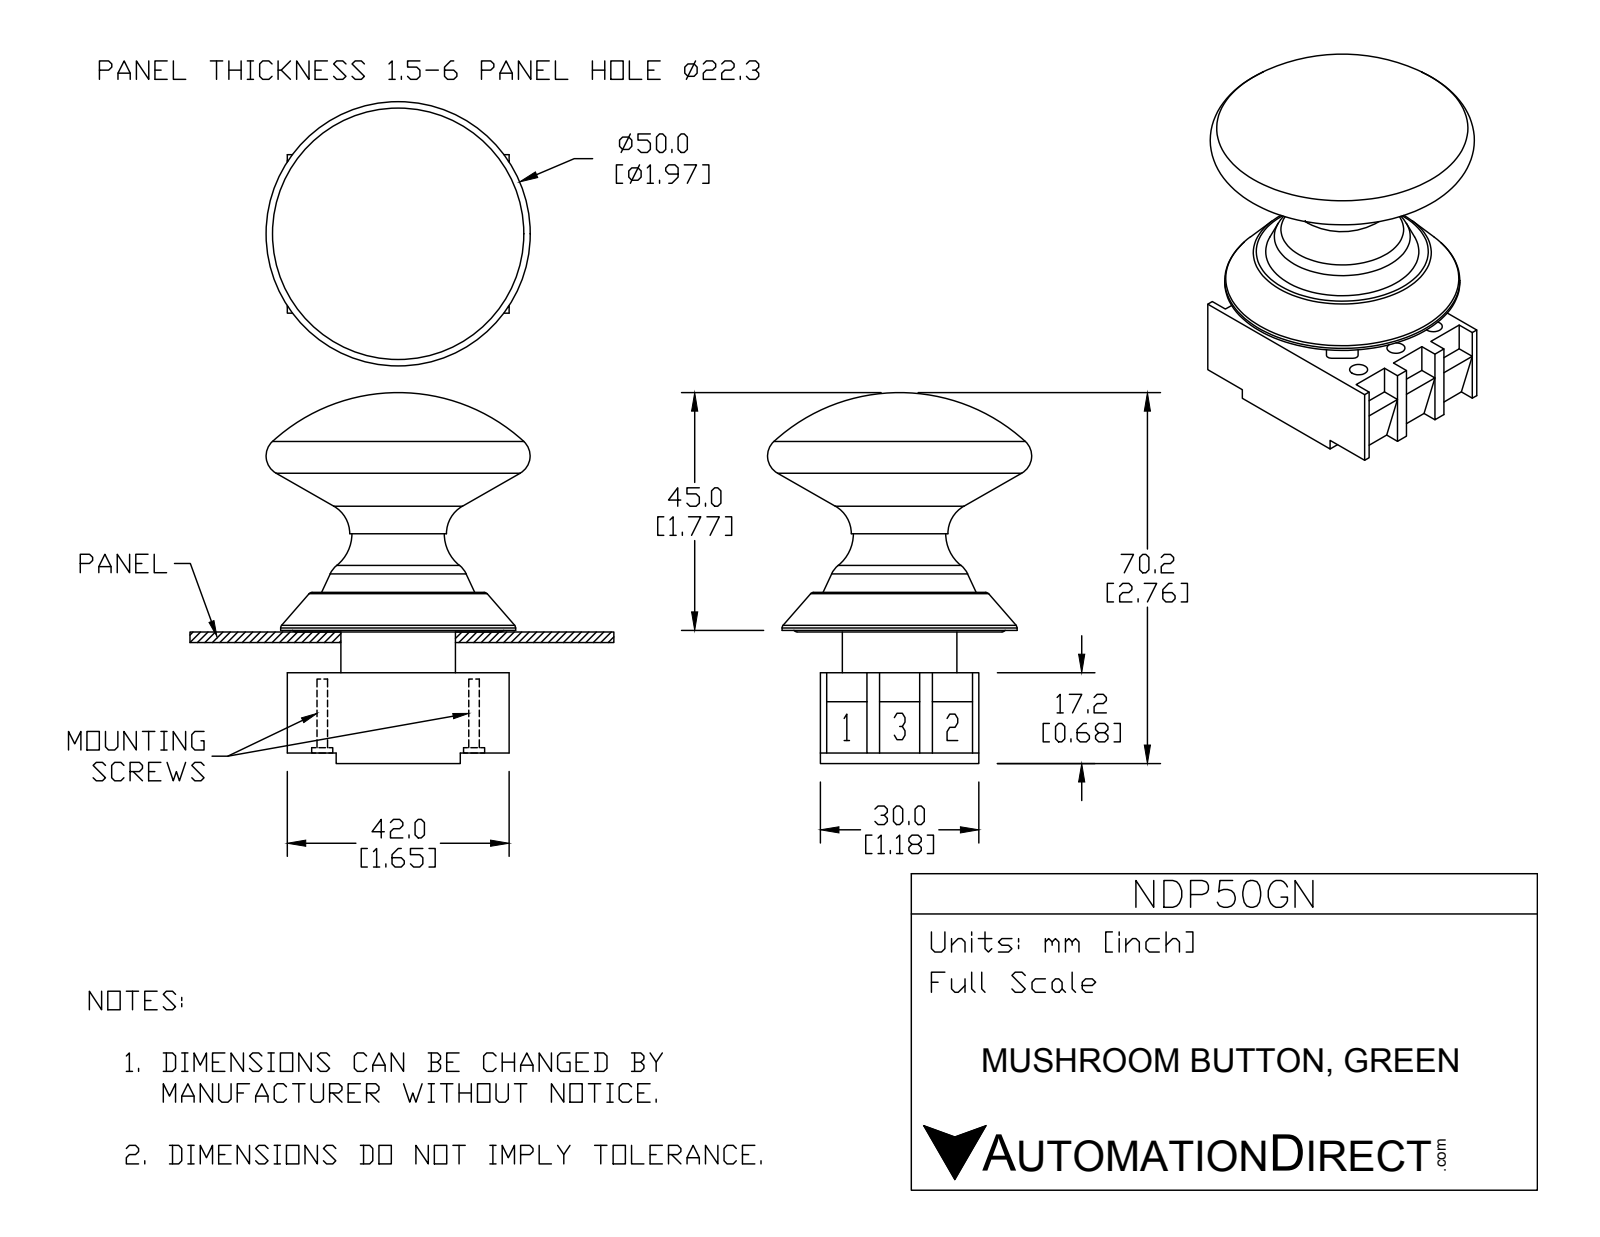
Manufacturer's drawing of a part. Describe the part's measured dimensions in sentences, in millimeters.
The part is named "NDP50GN". Its 3-D file was written by "SolidWorks 2015 (AUTOMOTIVE_DESIGN)". It is 7 solids with 222 faces: 126 planar, 63 cylindrical and 33 other. Overall it measures 70.2 by 50 by 50 millimeters. Its volume is 55 695 cubic millimeters and its surface area 21 605 square millimeters. Round holes: 6 of diameter 3.4, 6 of diameter 5, 1 of diameter 12.5. Round bosses or shafts: 2 of diameter 4.6, 2 of diameter 4, 1 of diameter 44.5, 1 of diameter 21.7. Partial cylindrical surfaces (rounded edges, fillets, slot ends): 8 of radius 1, 5 of radius 8.7, 1 of radius 11. The main face-to-face distances are 7.2, 15.2, 30, 8, 7.5, 7.7, 22.9, 10, 23.2, 30.4. The hole center spacings are 10, 17.52, 30.45, 28.76, 14.38, 20, 35.03.
